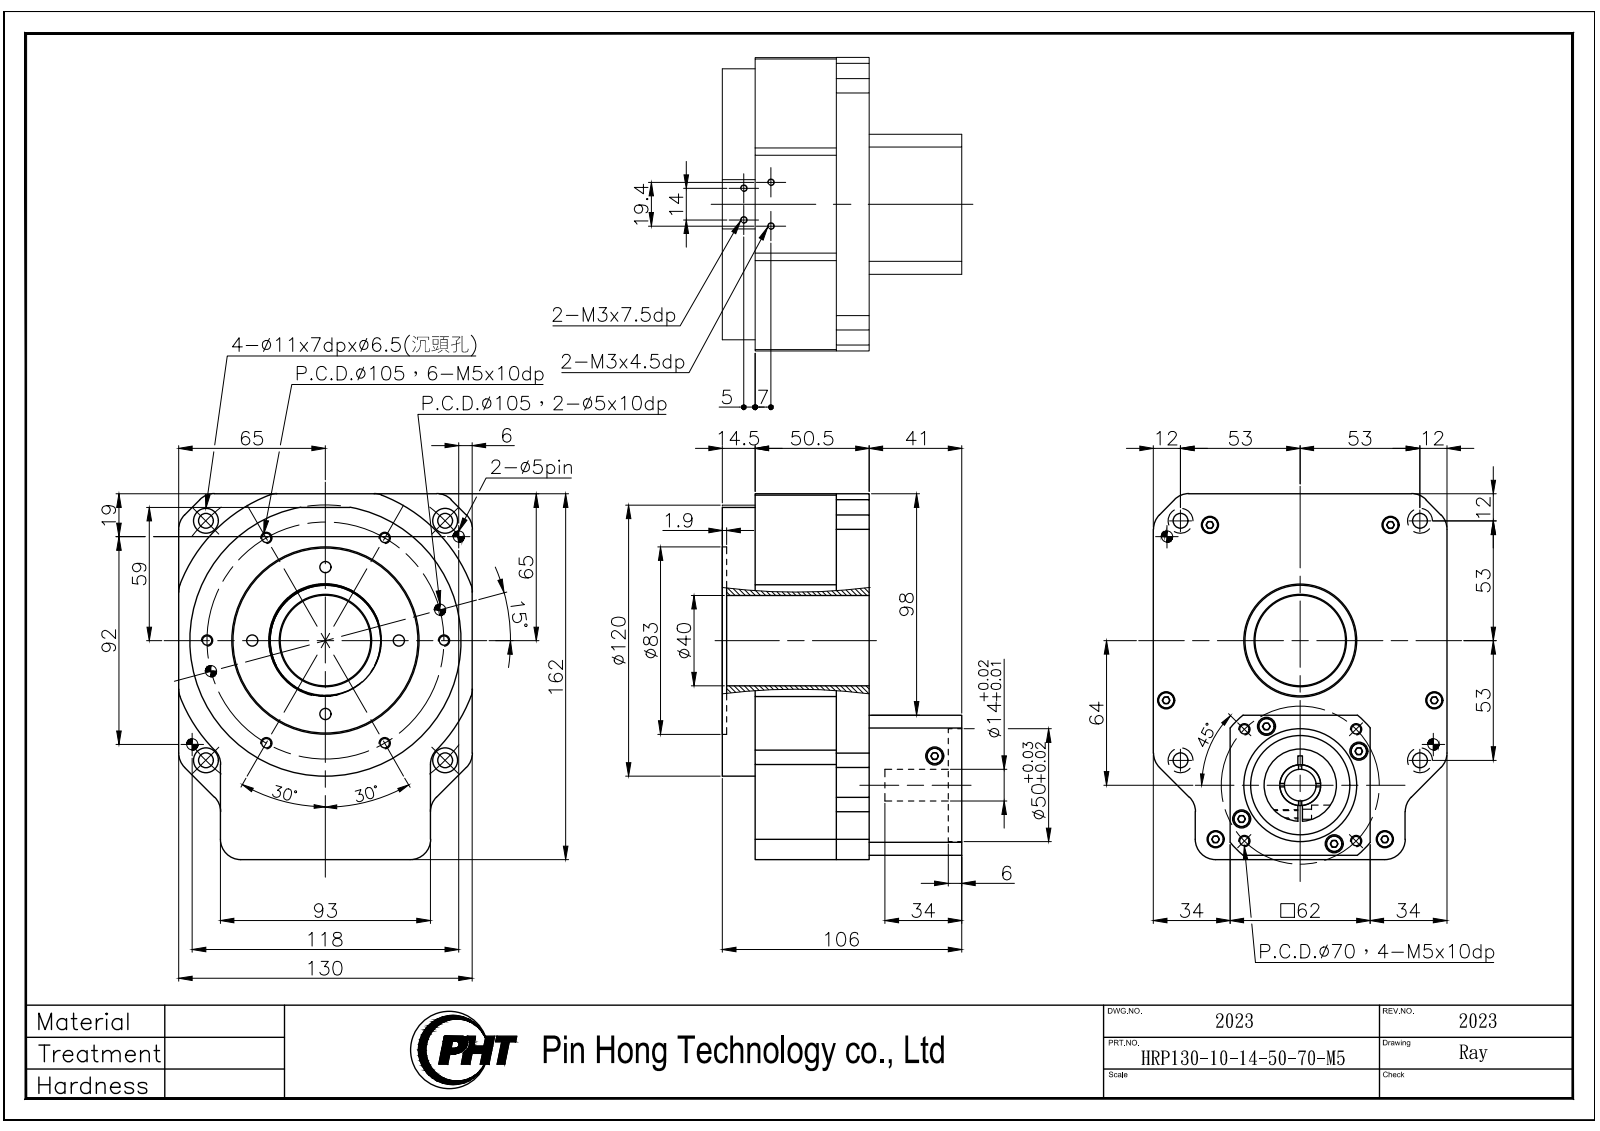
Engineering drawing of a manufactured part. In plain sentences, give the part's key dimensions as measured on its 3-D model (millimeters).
The part is named "HRP130-10-14-50-70-M5_2023". Its 3-D file was written by "SolidWorks 2016 (CONFIG_CONTROL_DESIGN)". It is 1 solid with 414 faces: 181 planar, 185 cylindrical and 48 other. Overall it measures 162 by 130 by 106 millimeters. Its volume is 1 107 000 cubic millimeters and its surface area 107 287 square millimeters. Round holes: 16 of diameter 4.2, 8 of diameter 5, 6 of diameter 7.5, 6 of diameter 8, 4 of diameter 2.5, 4 of diameter 4.3, 4 of diameter 6.5, 4 of diameter 11, 2 of diameter 50, 1 of diameter 3.3, 1 of diameter 4.5, 1 of diameter 14. Round bosses or shafts: 10 of diameter 7, 1 of diameter 120, 1 of diameter 82, 1 of diameter 32, 1 of diameter 20, 1 of diameter 18. Partial cylindrical surfaces (rounded edges, fillets, slot ends): 20 of radius 9, 1 of radius 4, 1 of radius 40, 1 of radius 69. The main face-to-face distances are 50.5, 14.5, 65, 62, 1.9, 63.1, 12.6, 96, 33.95, 95.95. The hole center spacings are 52.5, 9.83, 27.32, 27.79, 30, 35, 39.77, 42.43.
